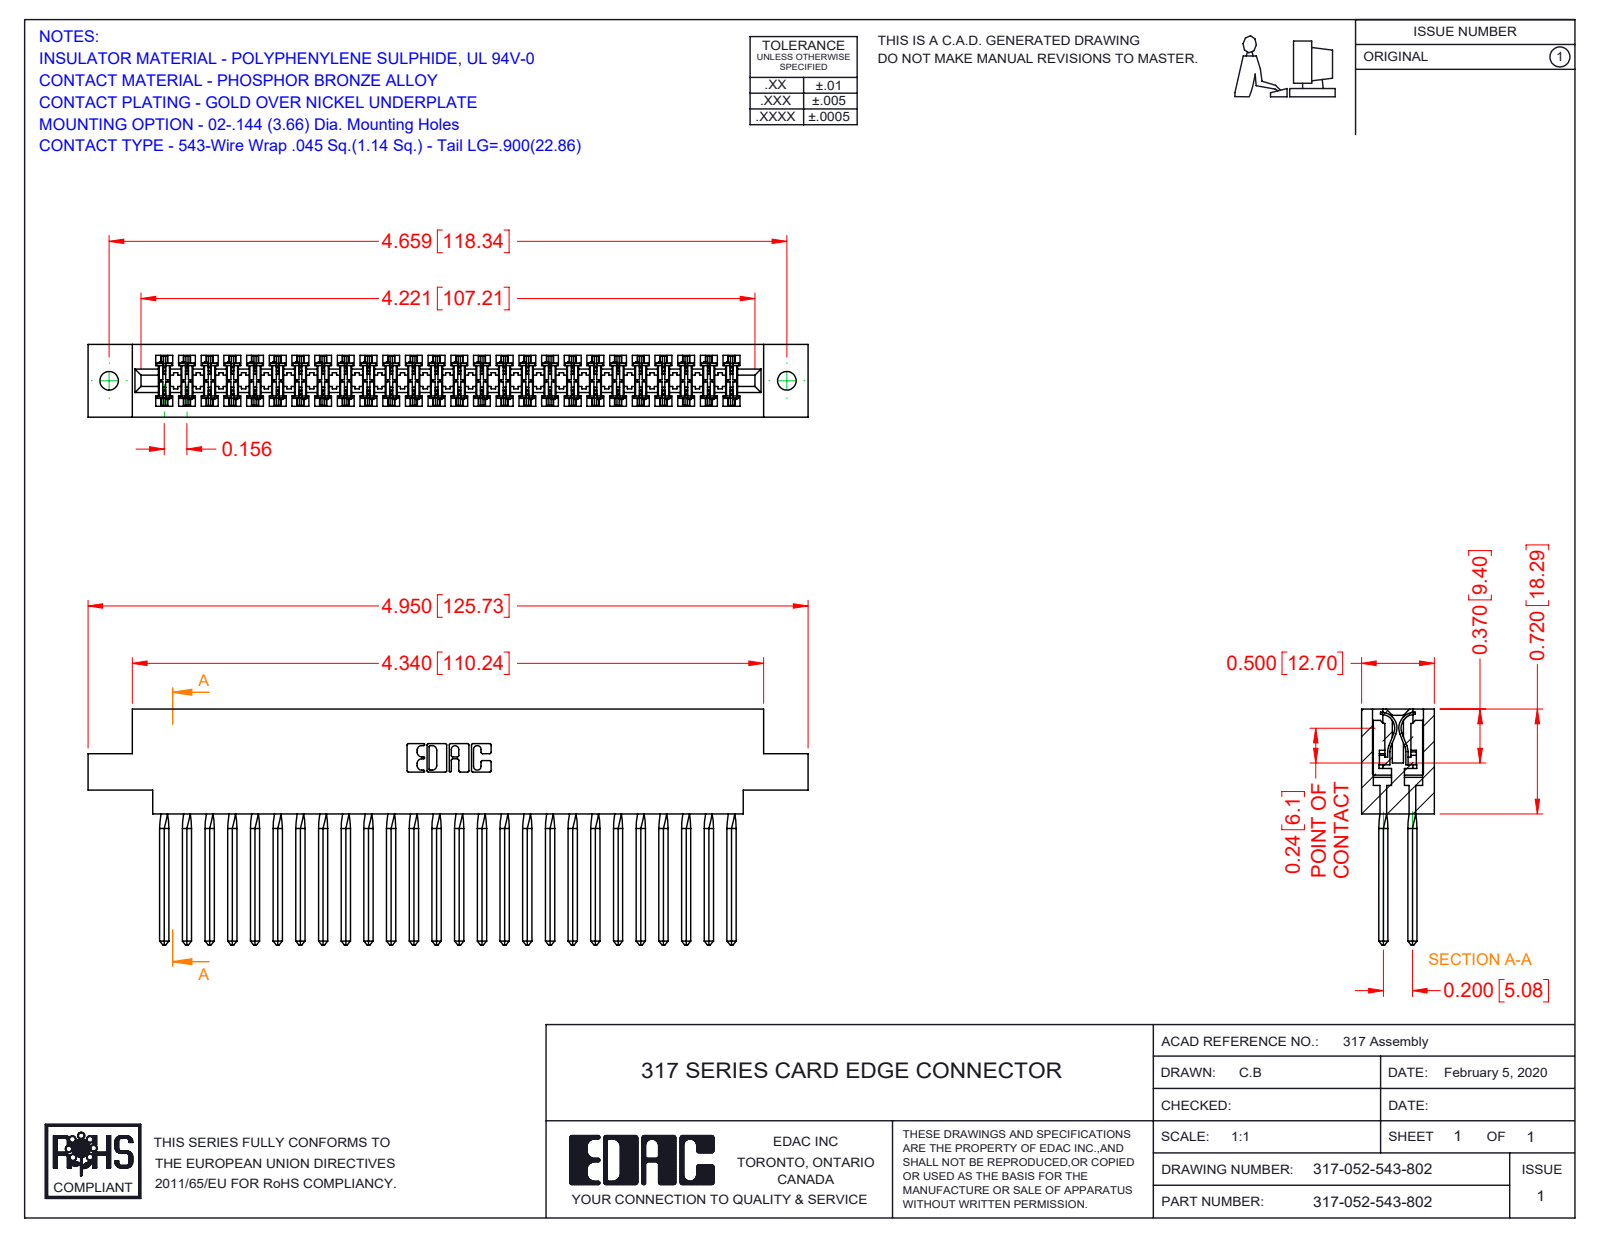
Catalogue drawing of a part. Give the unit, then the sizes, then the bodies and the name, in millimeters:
Units: millimetres
Overall size (bounding box): 125.7 × 41.1 × 12.7
Round holes (diameter × count): ⌀3.3 ×2
Partial cylindrical surfaces — rounded edges, fillets, slot ends (radius × count): R0.4 ×104, R0.3 ×22, R0.2 ×6, R0.8 ×6, R0.7 ×3, R2.4 ×2, R2.5 ×2, R2.8 ×2
Main face-to-face distances: 12.7, 1.9, 10.8, 2.8, 8.9, 5, 2.4, 18.3, 5.1, 2.9
Hole centre spacings: 118.3
Volume: 20 780 mm³ · Surface area: 30 640 mm²
Bodies: 53 solids, 4730 faces (3854 planar, 668 cylindrical, 208 other)
Part name (STEP PRODUCT): 317-290-001_543; 317 Part_.144 Dia; 317-052-543-802
STEP written by: SolidWorks 2016 (CONFIG_CONTROL_DESIGN)
